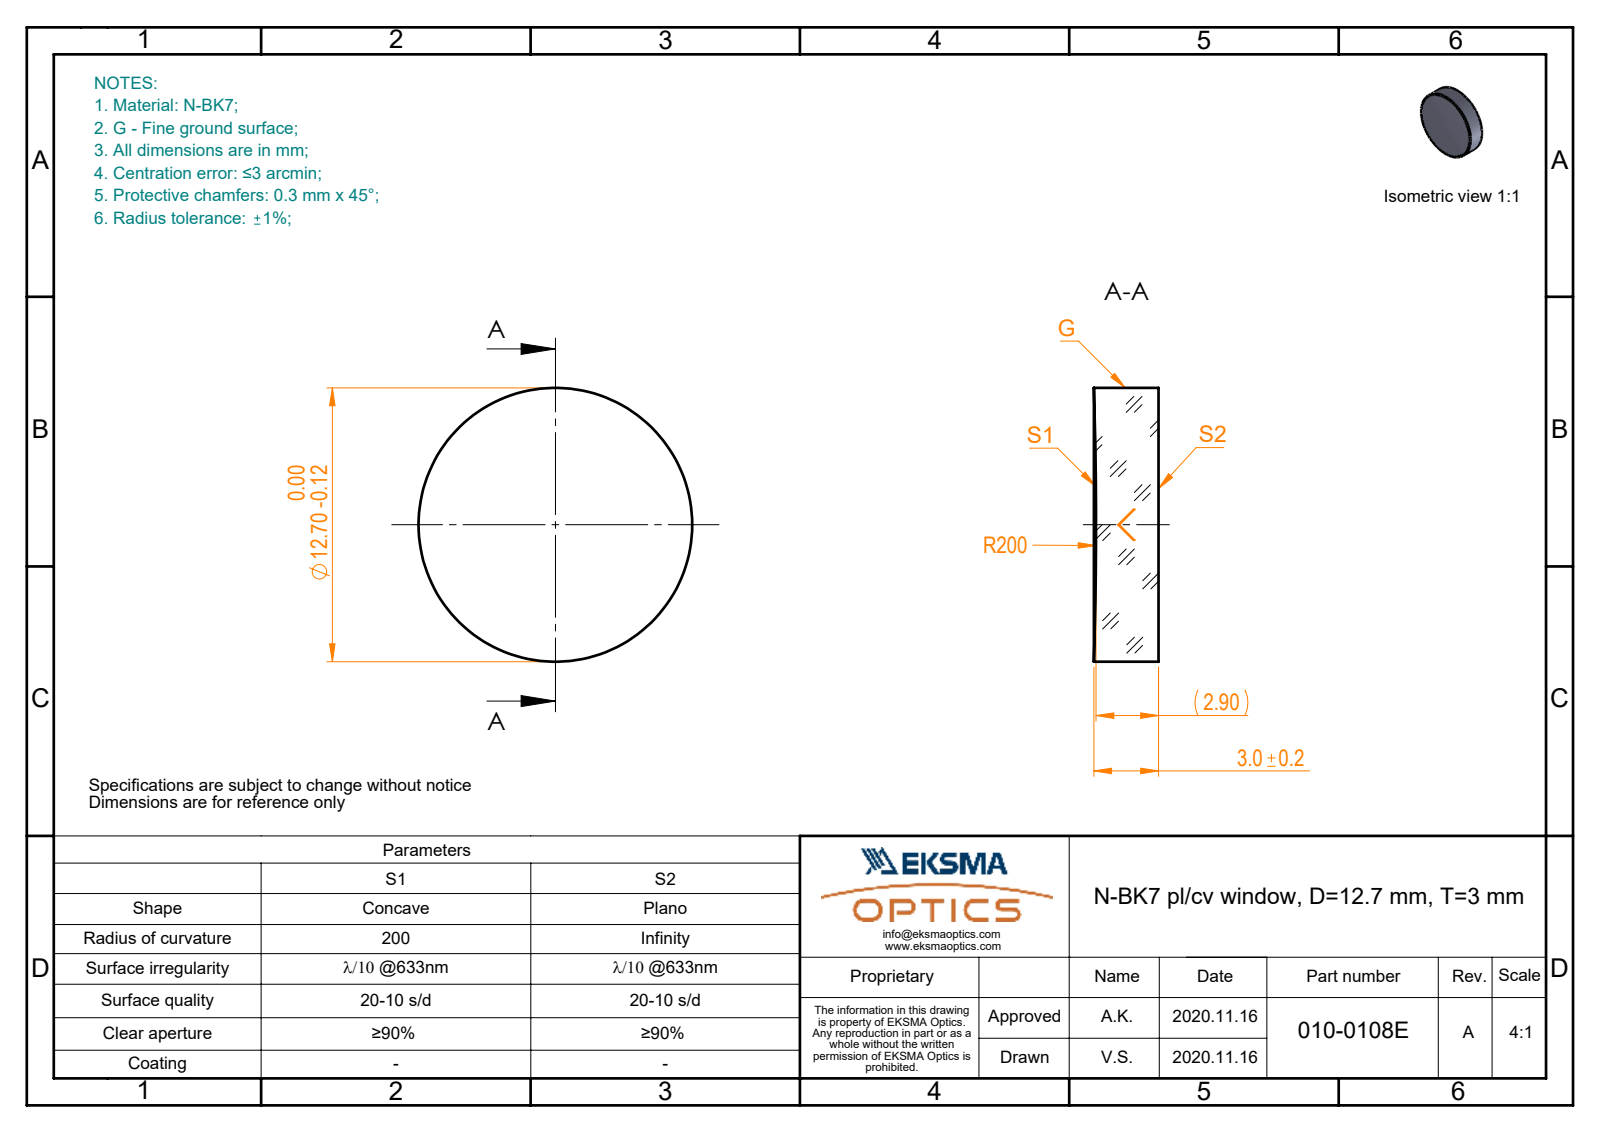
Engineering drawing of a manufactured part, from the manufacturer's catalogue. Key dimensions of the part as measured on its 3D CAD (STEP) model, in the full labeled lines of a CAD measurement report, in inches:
Part name (STEP PRODUCT): 010-0108E_N-BK7_PCV_window
STEP written by: SolidWorks 2019 (CONFIG_CONTROL_DESIGN)
Units: inches
Bodies: 1 solid, 5 faces (1 planar, 2 cylindrical, 2 other)
Overall size (bounding box): 0.5 × 0.5 × 0.118
Volume: 0.023 in³ · Surface area: 0.578 in²
Round bosses / shafts (diameter × count): ⌀0.5 ×1
